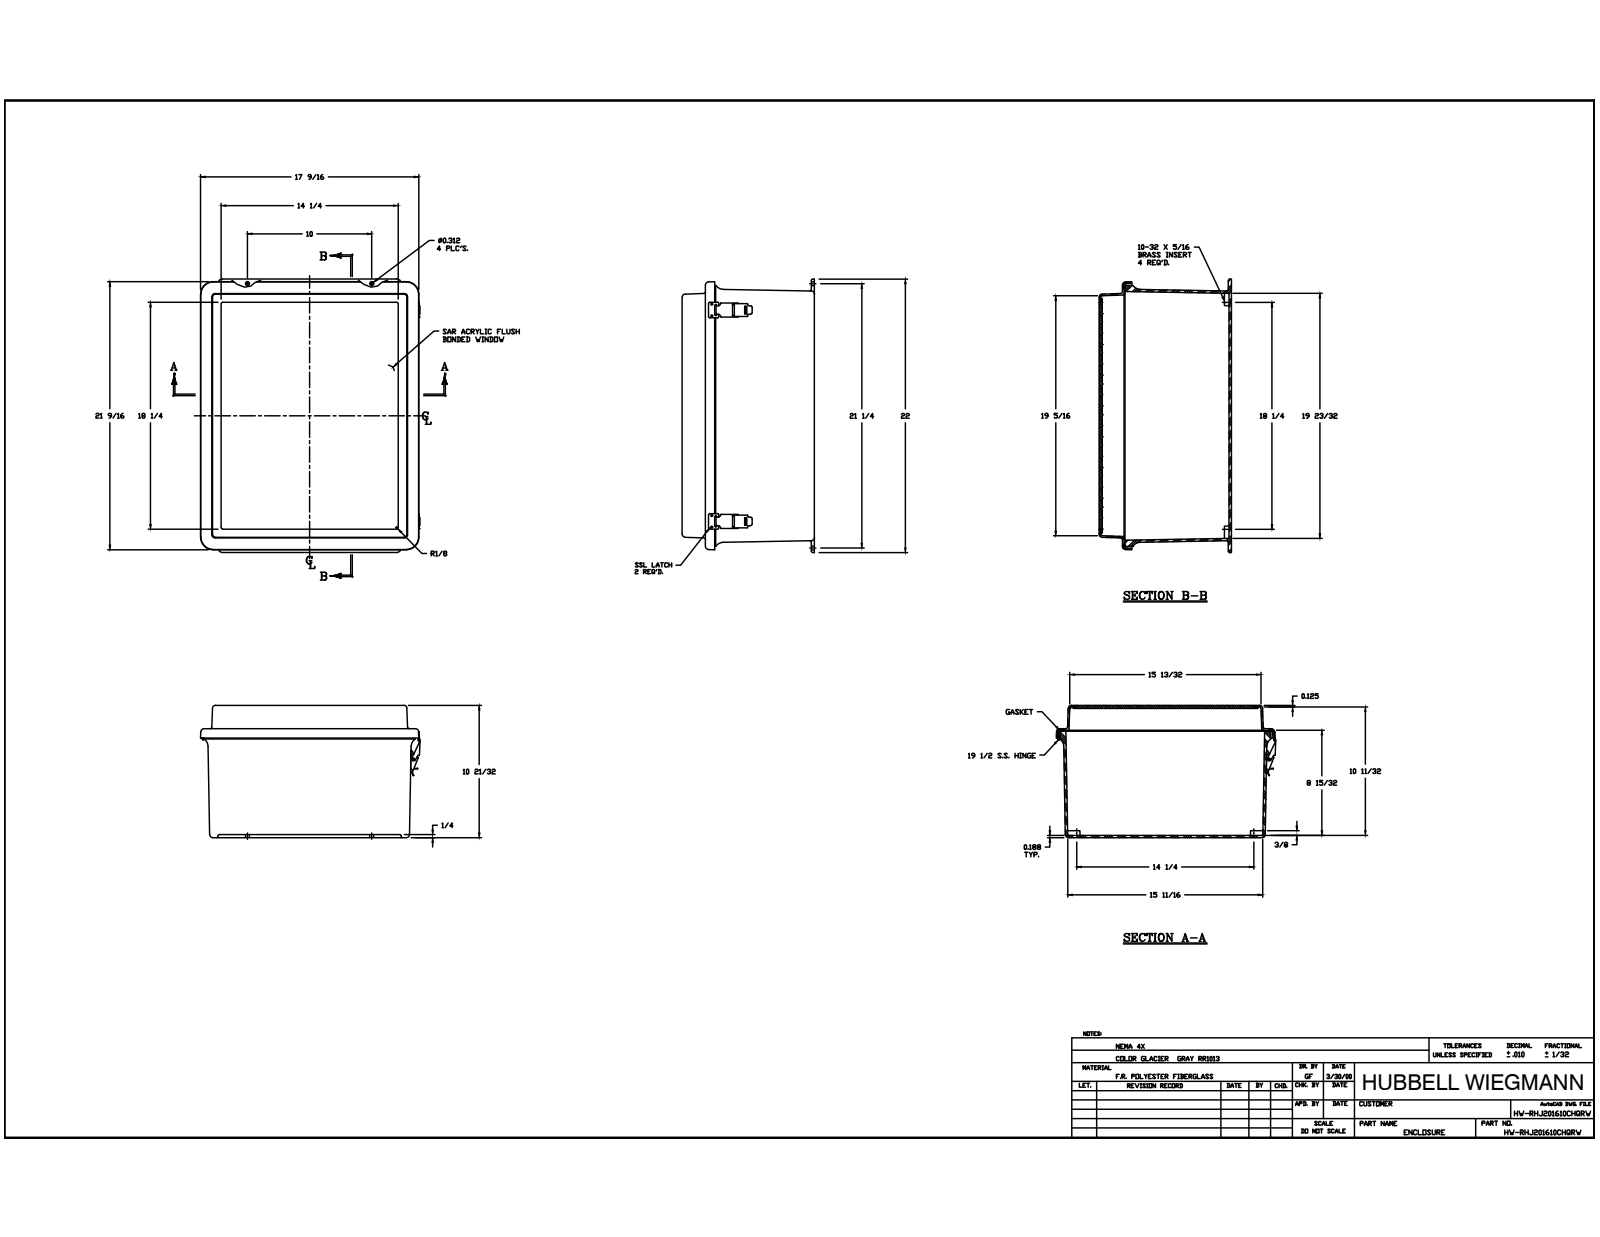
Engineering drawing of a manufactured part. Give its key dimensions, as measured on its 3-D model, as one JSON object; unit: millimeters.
{"part_name": "J2016HL_3; RMINS45821P_45; RMINS45821P_46; RMINS45821P_47 (+8 more)", "step_written_by": "Autodesk Inventor 2014 (AUTOMOTIVE_DESIGN)", "units": "millimeters", "bodies": {"solids": 43, "faces": 1242, "planar": 558, "cylindrical": 517, "other": 167}, "overall_size": [558.8, 449.53, 270.3], "volume_mm3": 5021000, "surface_area_mm2": 2102000, "round_holes": [[3.56, 24], [3.33, 12], [2.64, 8], [3.86, 5], [3.3, 4], [3.96, 4], [5.54, 4], [3.43, 2], [9.52, 2], [2.16, 1]], "round_bosses_or_shafts": [[3.17, 20], [6.35, 12], [6.86, 4], [7.62, 1], [4.31, 1], [3.94, 1], [3.05, 1]], "partial_cylinders_radius": [[3.17, 34], [0.38, 20], [0.79, 20], [1.14, 16], [6.35, 16], [0.76, 12], [0.57, 9], [1.52, 6]], "face_to_face_distances": [4.76, 4.77, 6.35, 263.95, 270.3, 265.53, 259.18, 3.17, 3.18, 44.45], "hole_center_spacings": [95.25, 431.8, 190.5, 23.81, 6.35, 88.9, 101.6, 184.15]}
